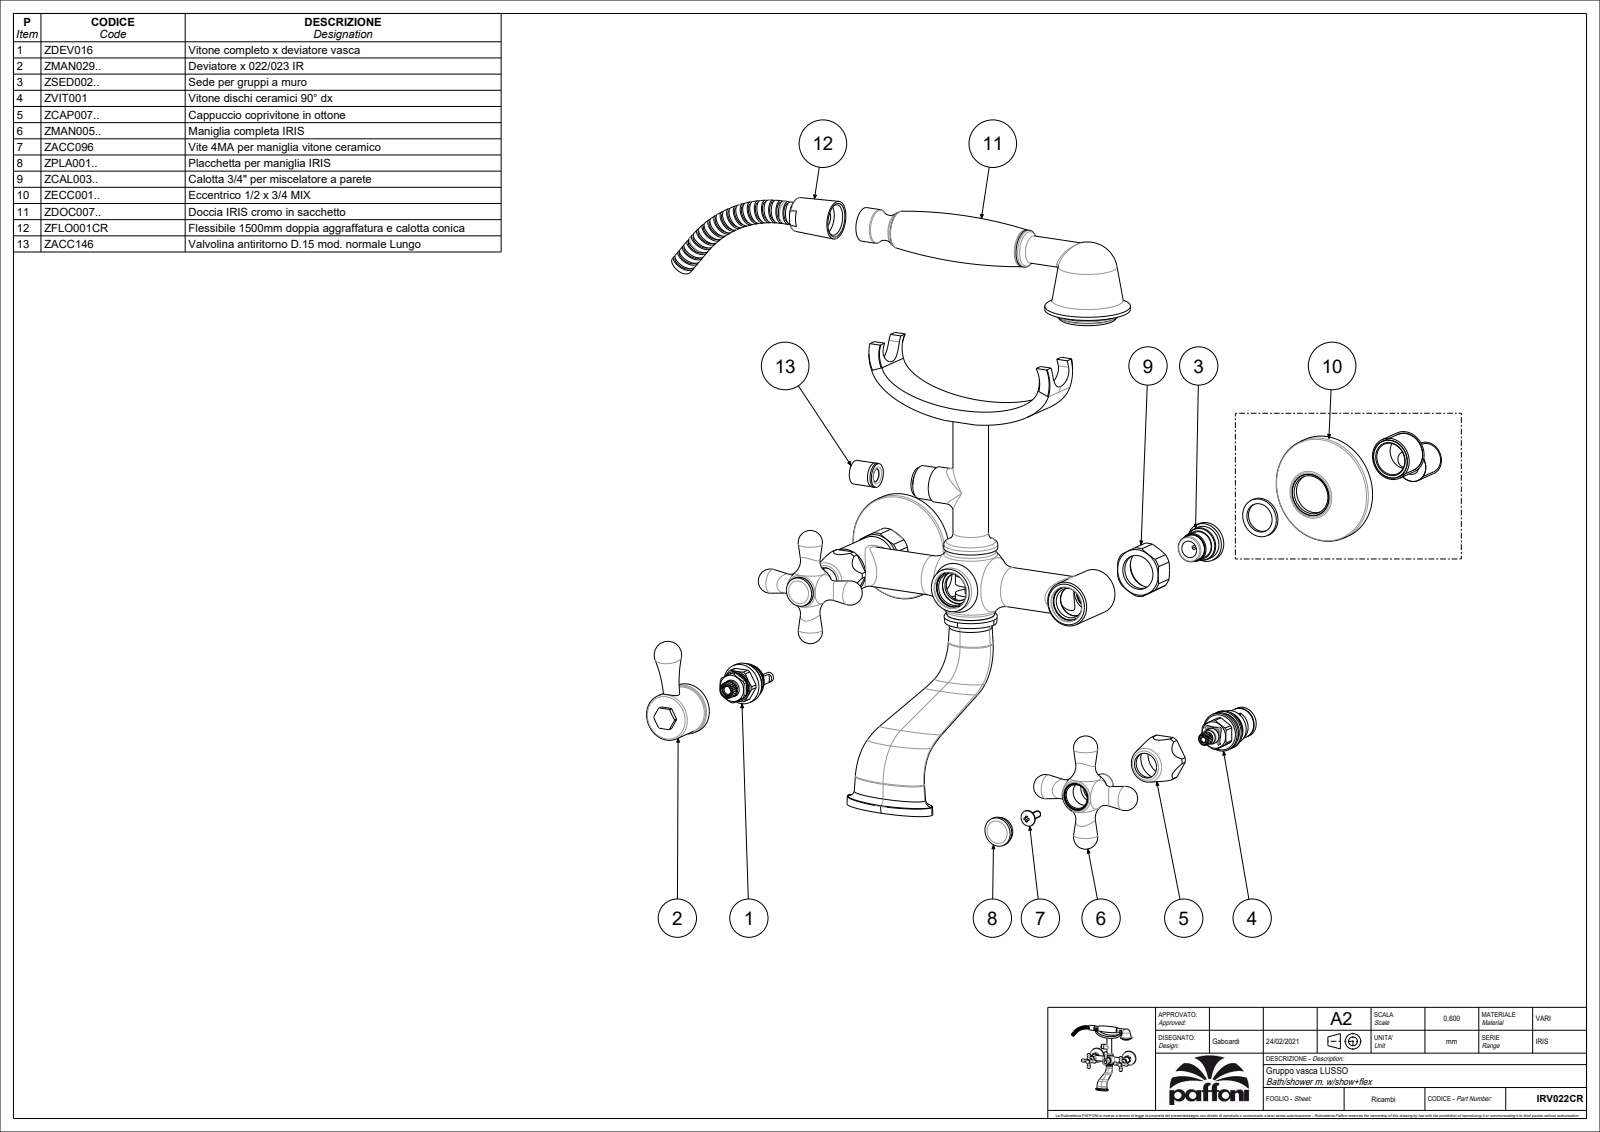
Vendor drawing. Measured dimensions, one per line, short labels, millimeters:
name: IRV022CR
written by: CREO PARAMETRIC BY PTC INC, 2020044 (CONFIG_CONTROL_DESIGN)
unit: mm
bodies: 3 solids, 526 faces (86 planar, 94 cylindrical, 346 other)
size: 302.3 × 280.51 × 165.32
volume: 658 554 mm³; area: 136 159 mm²
holes: 1× ⌀14
bosses: 3× ⌀20.5, 3× ⌀18, 2× ⌀65.5, 2× ⌀27.8, 2× ⌀22, 2× ⌀13.5, 1× ⌀53, 1× ⌀44
rounds: 2× R14.5, 2× R15.5, 1× R7.35, 1× R10
face distances: 26.5, 66.95, 40.45, 29, 227.01, 6.75, 233.01, 6, 33.7, 33.25
